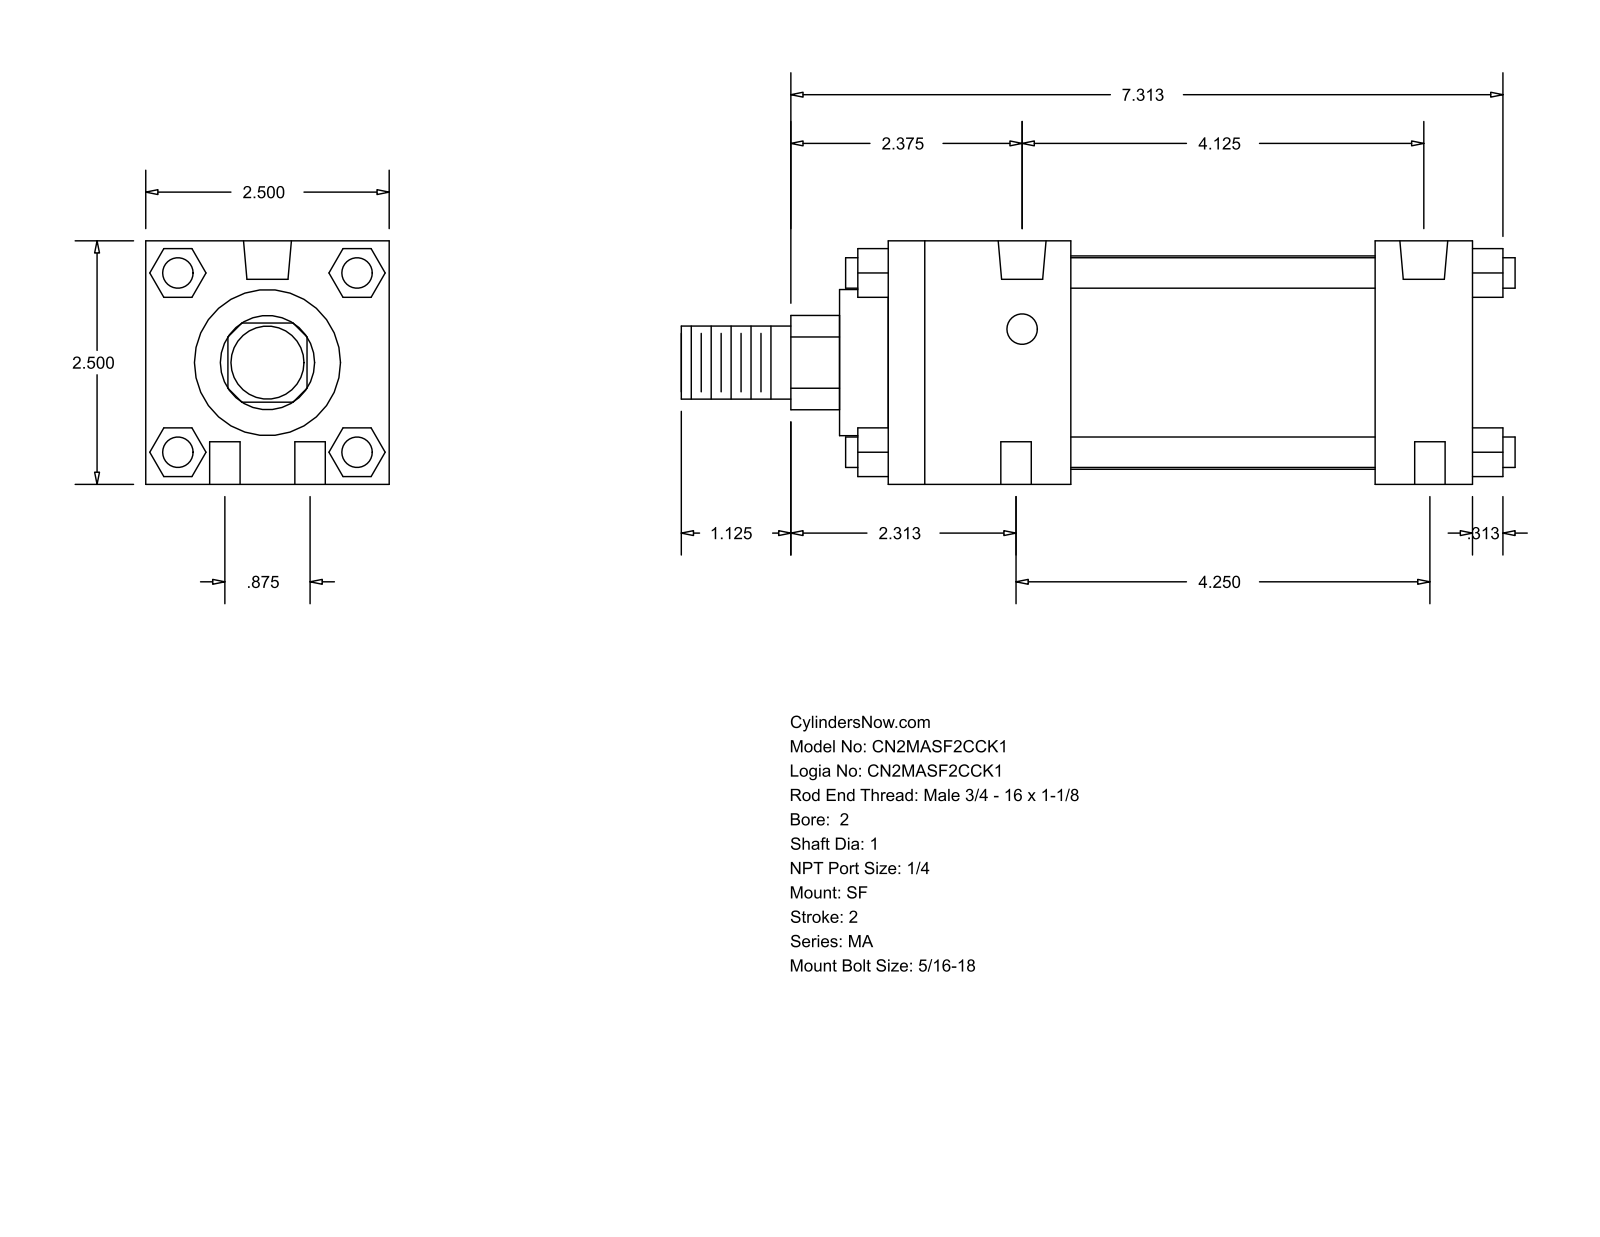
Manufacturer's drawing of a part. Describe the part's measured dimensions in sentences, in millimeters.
The part is named "MA_SF__0200_1". Its 3-D file was written by "GSSL Pune (CONFIG_CONTROL_DESIGN)". It is 0 solids with 124 faces: 94 planar, 30 cylindrical and 0 other. Overall it measures 217.49 by 63.5 by 63.5 millimeters. Round holes: 6 of diameter 7.94, 2 of diameter 12.49. Round bosses or shafts: 4 of diameter 7.94, 1 of diameter 55.63, 1 of diameter 38.1, 1 of diameter 25.4, 1 of diameter 19.05. Partial cylindrical surfaces (rounded edges, fillets, slot ends): 1 of radius 12.29. The main face-to-face distances are 63.5, 152.4, 12.7, 25.4, 127, 47.63, 79.37, 104.77, 40.47, 23.37. The hole center spacings are 11.22, 106.94, 22.22, 104.77, 107.95, 110.21.
